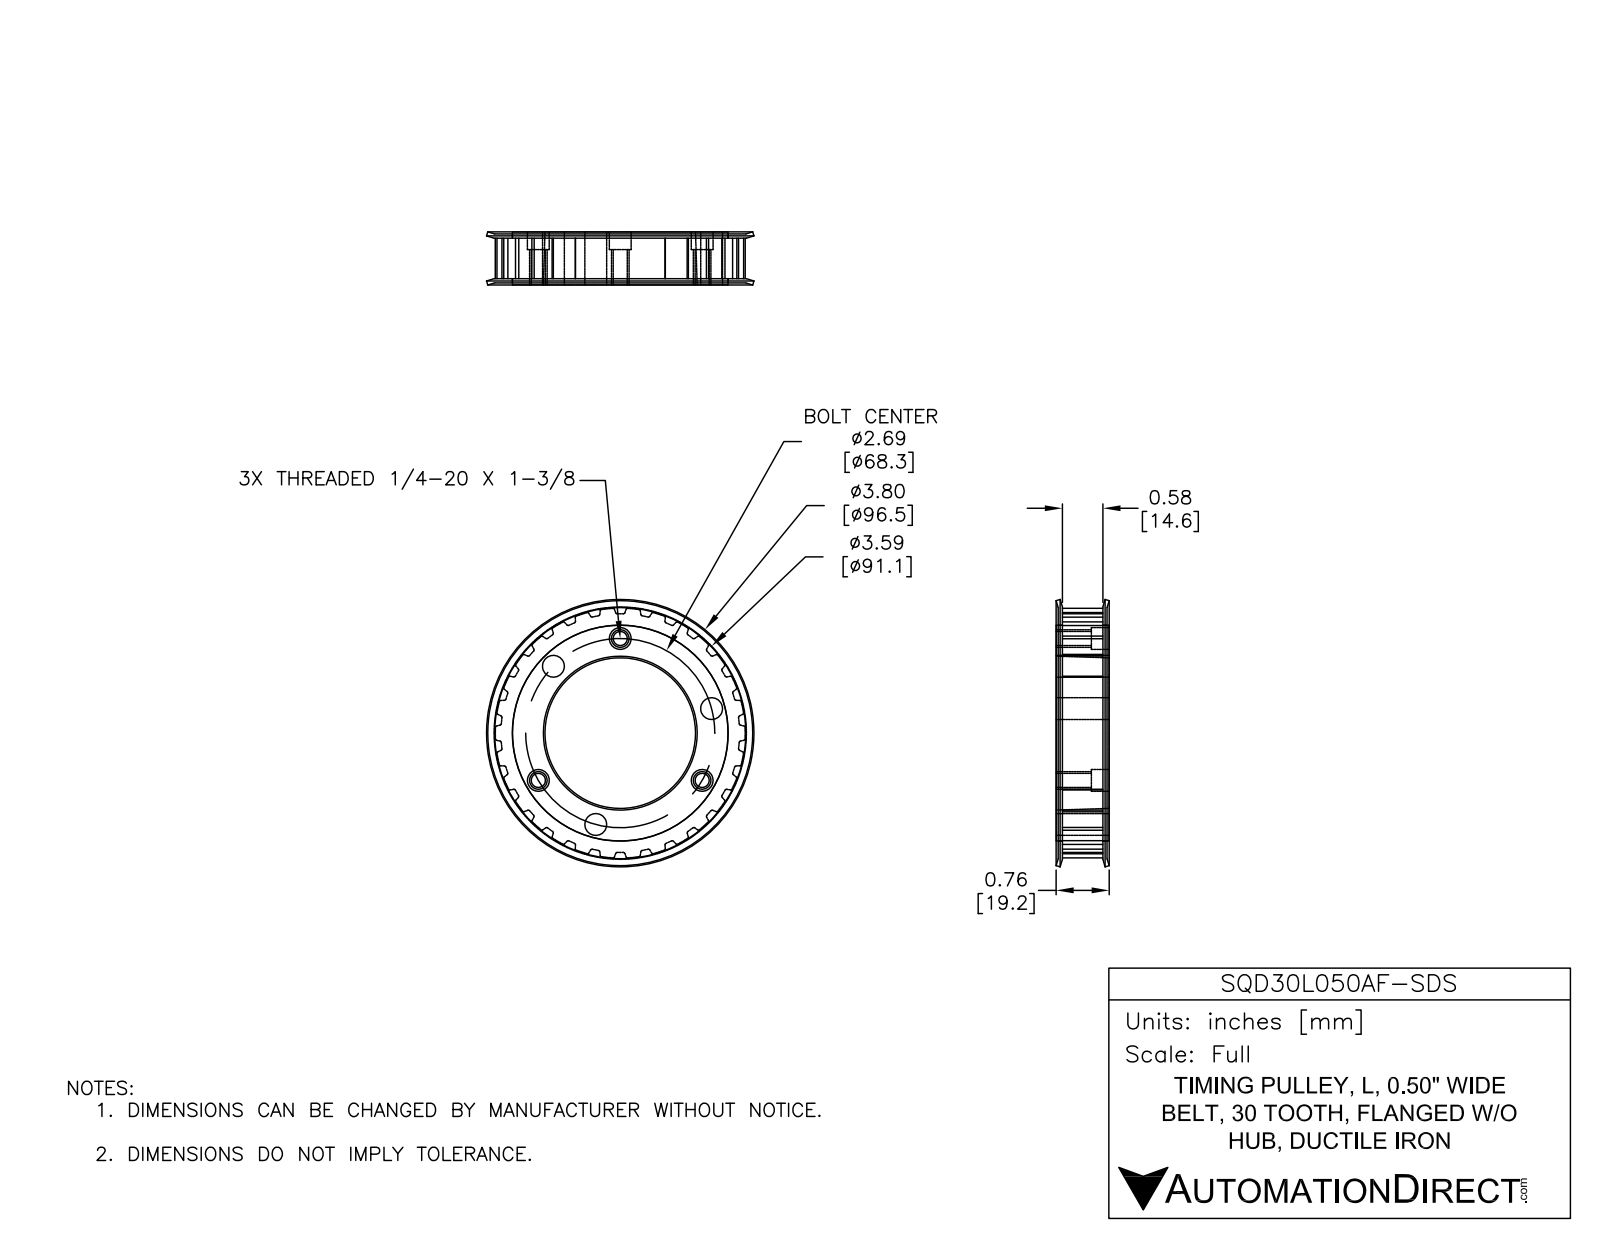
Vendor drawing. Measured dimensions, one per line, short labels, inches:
name: SQD30L050AF-SDS
written by: SolidWorks 2018 (AUTOMOTIVE_DESIGN)
unit: in
bodies: 1 solid, 316 faces (101 planar, 201 cylindrical, 14 other)
size: 3.8 × 3.8 × 0.755
volume: 4.221 in³; area: 39.37 in²
holes: 6× ⌀0.31, 3× ⌀0.2, 1× ⌀3.067
bosses: 1× ⌀3.063
rounds: 60× R0.015, 60× R0.02, 1× R1.776
face distances: 0.028, 0.722, 0.75, 0.695, 0.087, 0.663, 0.06, 0.635, 0.575, 3.391
hole spacings: 2.328, 1.344, 1.636, 1.029, 1.344, 2.327, 2.665, 1.028
